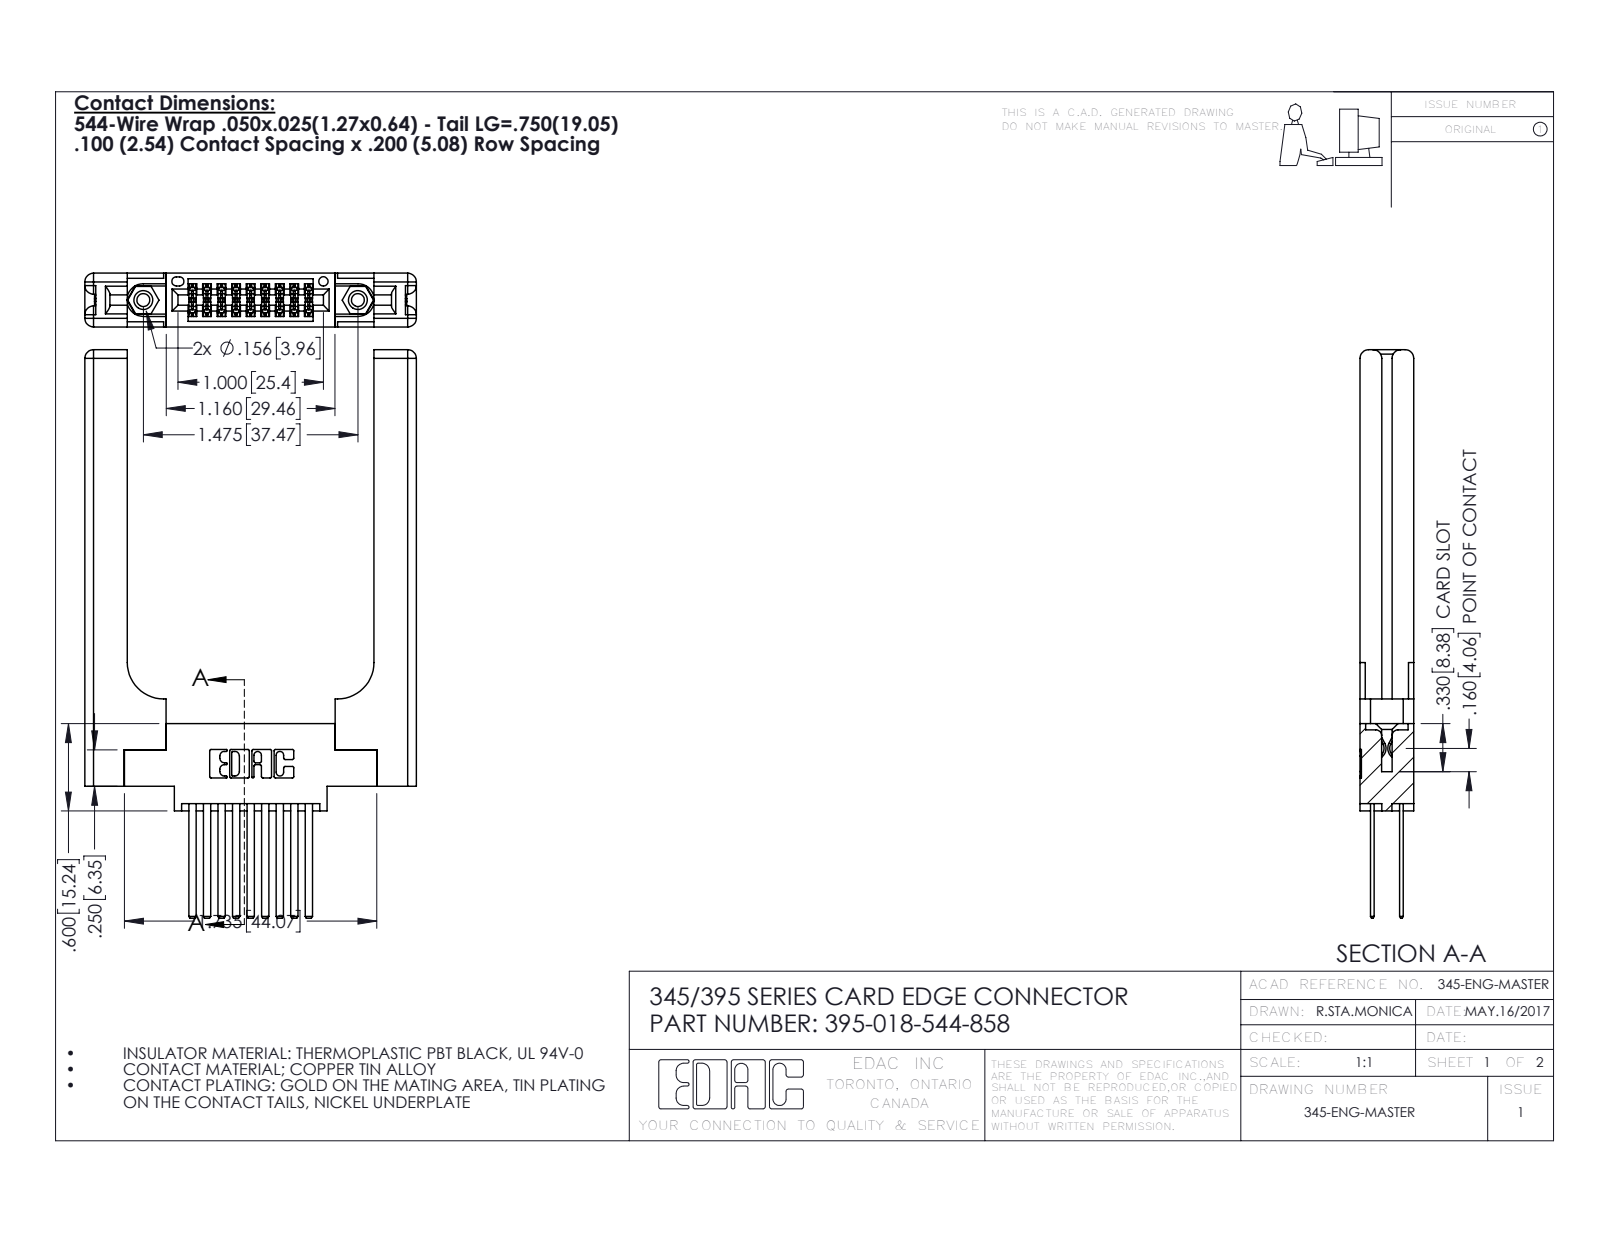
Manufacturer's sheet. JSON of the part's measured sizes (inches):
{"part_name": "345-250-001_345-250-001-102; 345-220-058_345-220-058; 345-292-001_345-293-144; 345 Part_0.170 Offset - 0.156 Dia-TH (+1 more)", "step_written_by": "SolidWorks 2016 (CONFIG_CONTROL_DESIGN)", "units": "inches", "bodies": {"solids": 23, "faces": 1178, "planar": 754, "cylindrical": 364, "other": 60}, "overall_size": [3.907, 2.279, 0.37], "volume_in3": 0.85, "surface_area_in2": 20.72, "round_holes": [[0.089, 2], [0.125, 2], [0.156, 2], [0.064, 1]], "round_bosses_or_shafts": [[0.155, 2]], "partial_cylinders_radius": [[0.006, 27], [0.01, 22], [0.06, 16], [0.007, 6], [0.031, 6], [0.026, 3], [0.014, 2], [0.019, 2]], "face_to_face_distances": [0.37, 0.072, 0.298, 0.15, 0.077, 0.148, 0.098, 0.272, 0.025, 0.2], "hole_center_spacings": [0.27, 1.244, 1.475]}
